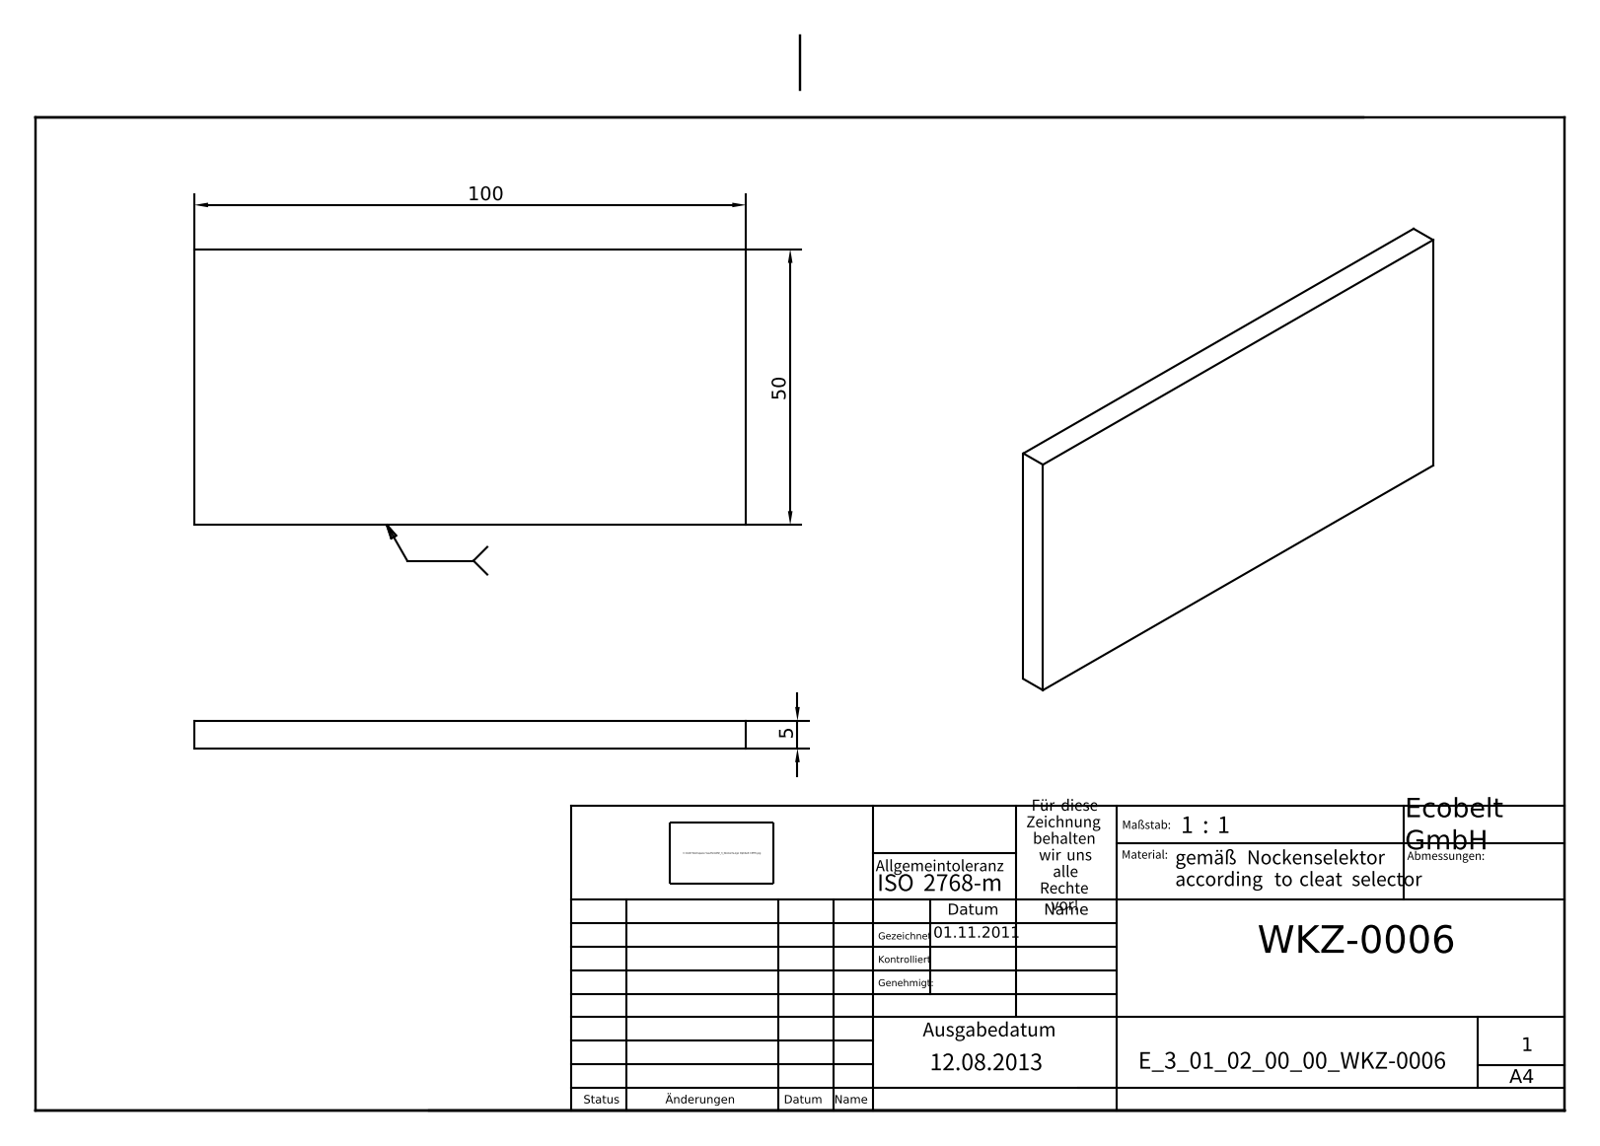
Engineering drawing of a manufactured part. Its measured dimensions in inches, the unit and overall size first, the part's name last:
Units: inches
Overall size (bounding box): 3.937 × 1.969 × 0.197
Main face-to-face distances: 0.197, 1.969, 3.937
Volume: 1.526 in³ · Surface area: 17.83 in²
Bodies: 1 solid, 6 faces (6 planar, 0 cylindrical, 0 other)
Part name (STEP PRODUCT): E_3_01_02_00_00_WKZ-0006
STEP written by: Autodesk Inventor 2021 (AUTOMOTIVE_DESIGN)
